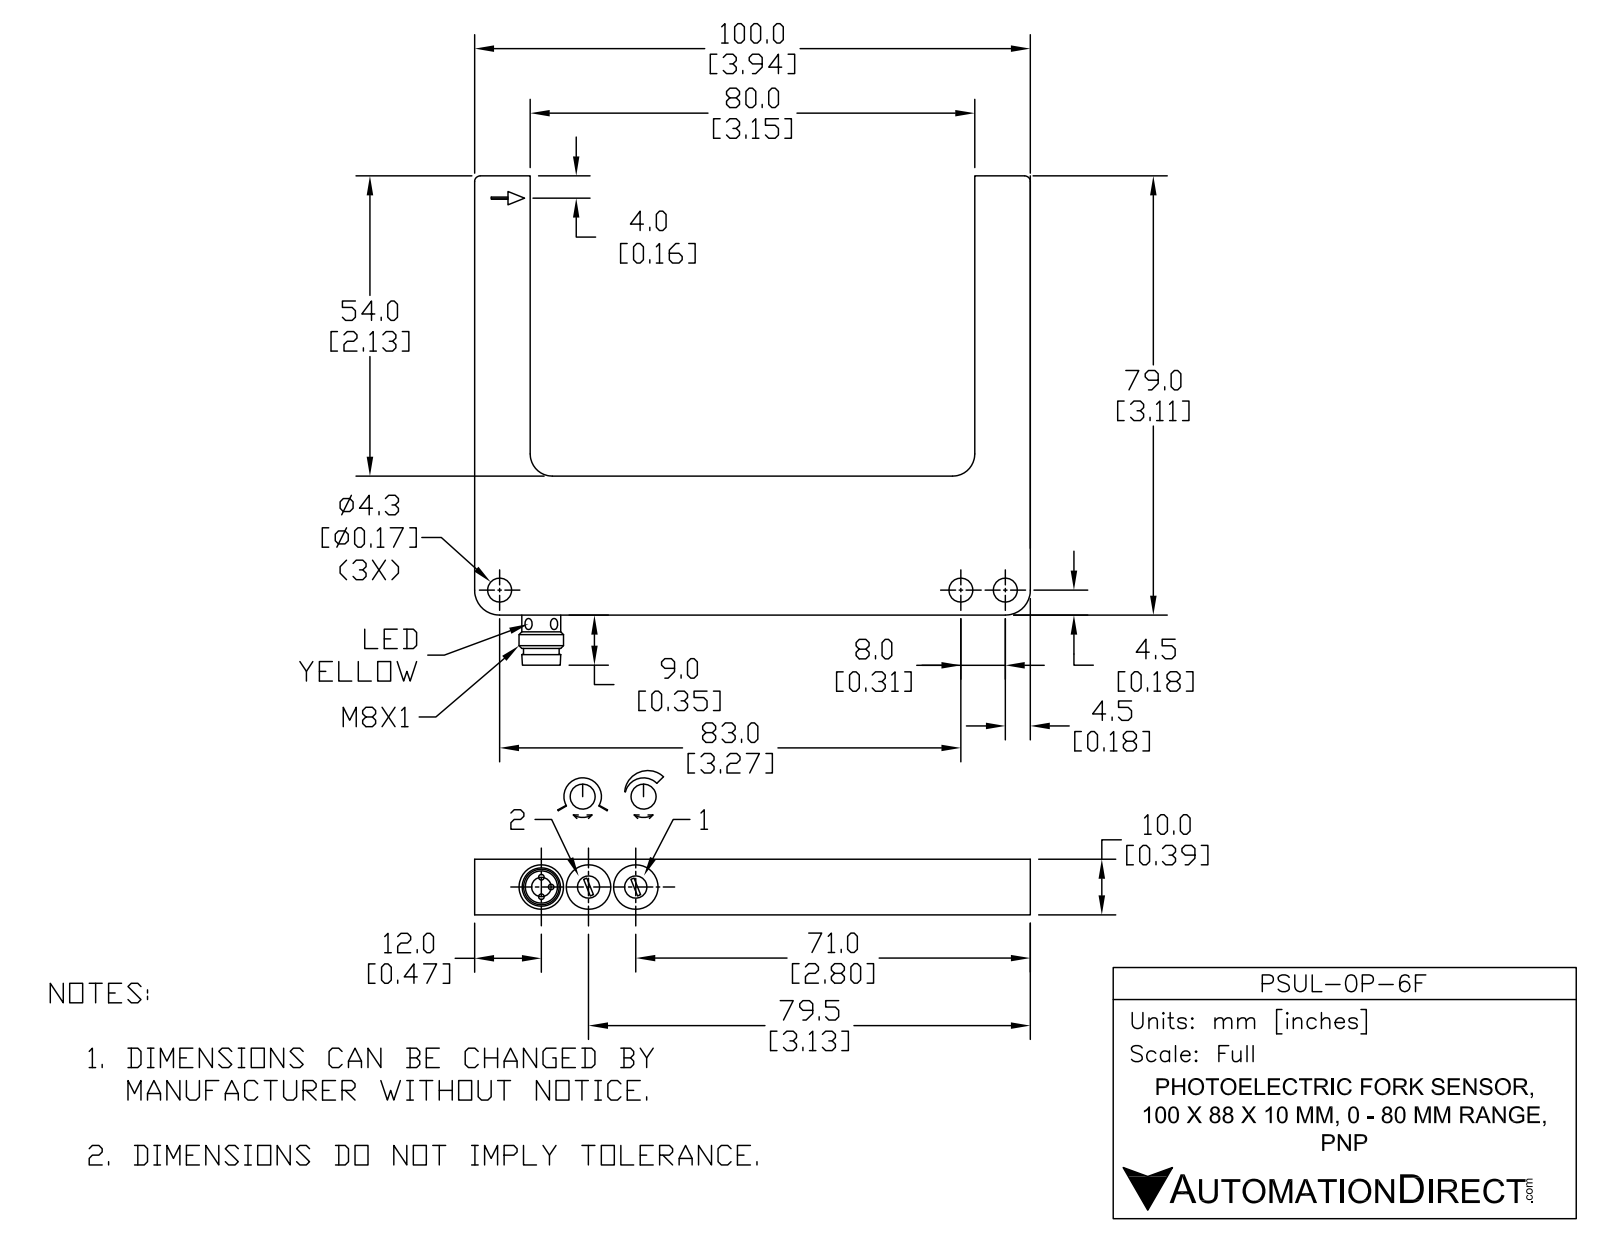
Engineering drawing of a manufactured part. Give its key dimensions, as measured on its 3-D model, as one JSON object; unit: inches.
{"part_name": "PSUL-0P-6F", "step_written_by": "SolidWorks 2019 (AUTOMOTIVE_DESIGN)", "units": "inches", "bodies": {"solids": 1, "faces": 95, "planar": 35, "cylindrical": 48, "other": 12}, "overall_size": [3.937, 3.465, 0.394], "volume_in3": 2.17, "surface_area_in2": 19.25, "round_holes": [[0.169, 3], [0.079, 2], [0.157, 2], [0.315, 2], [0.228, 1]], "round_bosses_or_shafts": [[0.039, 3], [0.315, 1], [0.267, 1]], "partial_cylinders_radius": [[0.02, 2], [0.039, 2], [0.063, 2], [0.157, 2], [0.177, 2]], "face_to_face_distances": [0.394, 3.543, 3.937, 0.984, 3.15, 2.126, 3.11, 3.106, 0.98, 0.157], "hole_center_spacings": [0.335, 0.315, 0.669, 3.268, 3.583]}
